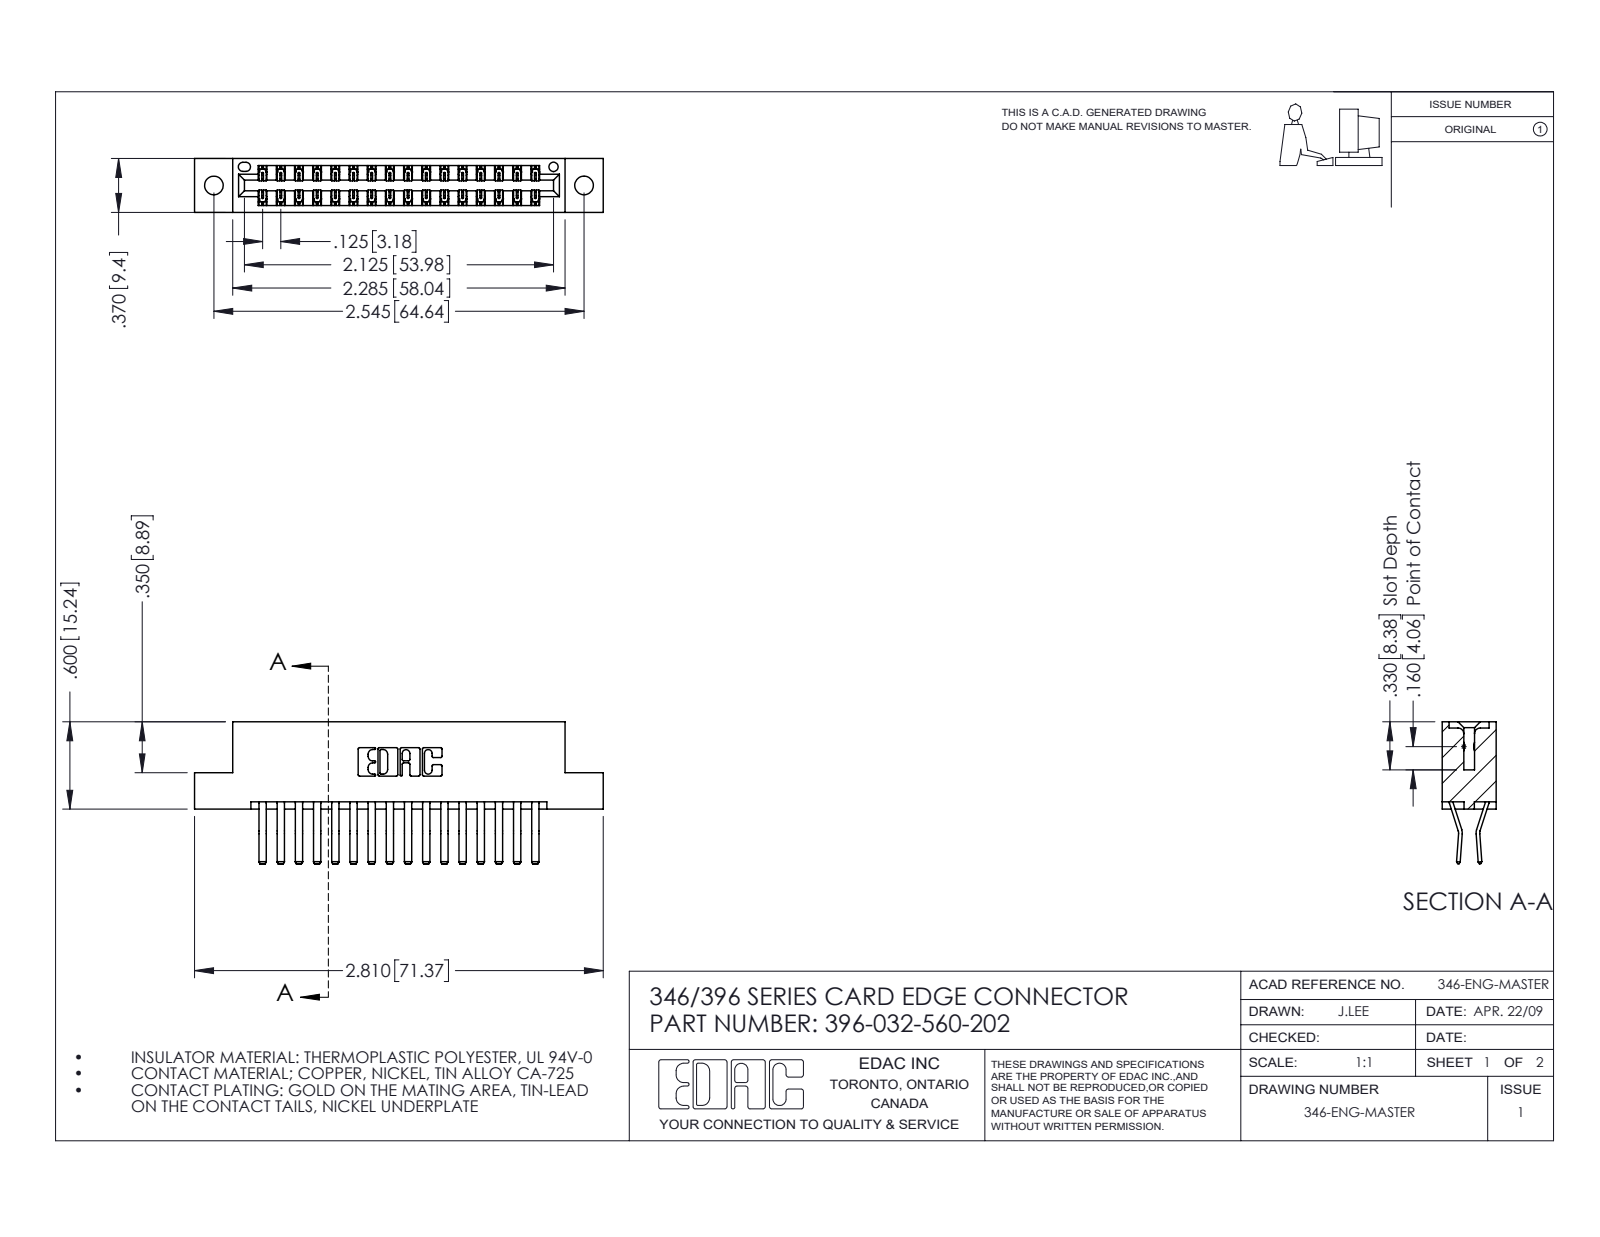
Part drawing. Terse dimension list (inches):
name: 346 Part_Flush Mounting Lugs - 0.128 Dia; 396-032-560-202; 345-292-001_560 Tail
written by: SolidWorks 2016 (CONFIG_CONTROL_DESIGN)
unit: in
bodies: 33 solids, 1850 faces (1196 planar, 654 cylindrical, 0 other)
size: 2.81 × 0.975 × 0.37
volume: 0.423 in³; area: 14.58 in²
holes: 2× ⌀0.128, 1× ⌀0.064
rounds: 48× R0.006, 22× R0.01, 6× R0.007, 6× R0.031, 3× R0.026, 2× R0.01, 2× R0.014, 2× R0.022
face distances: 0.048, 0.322, 0.25, 0.37, 0.025, 0.072, 0.298, 0.275, 0.148, 0.222
hole spacings: 0.246, 2.338, 2.545
